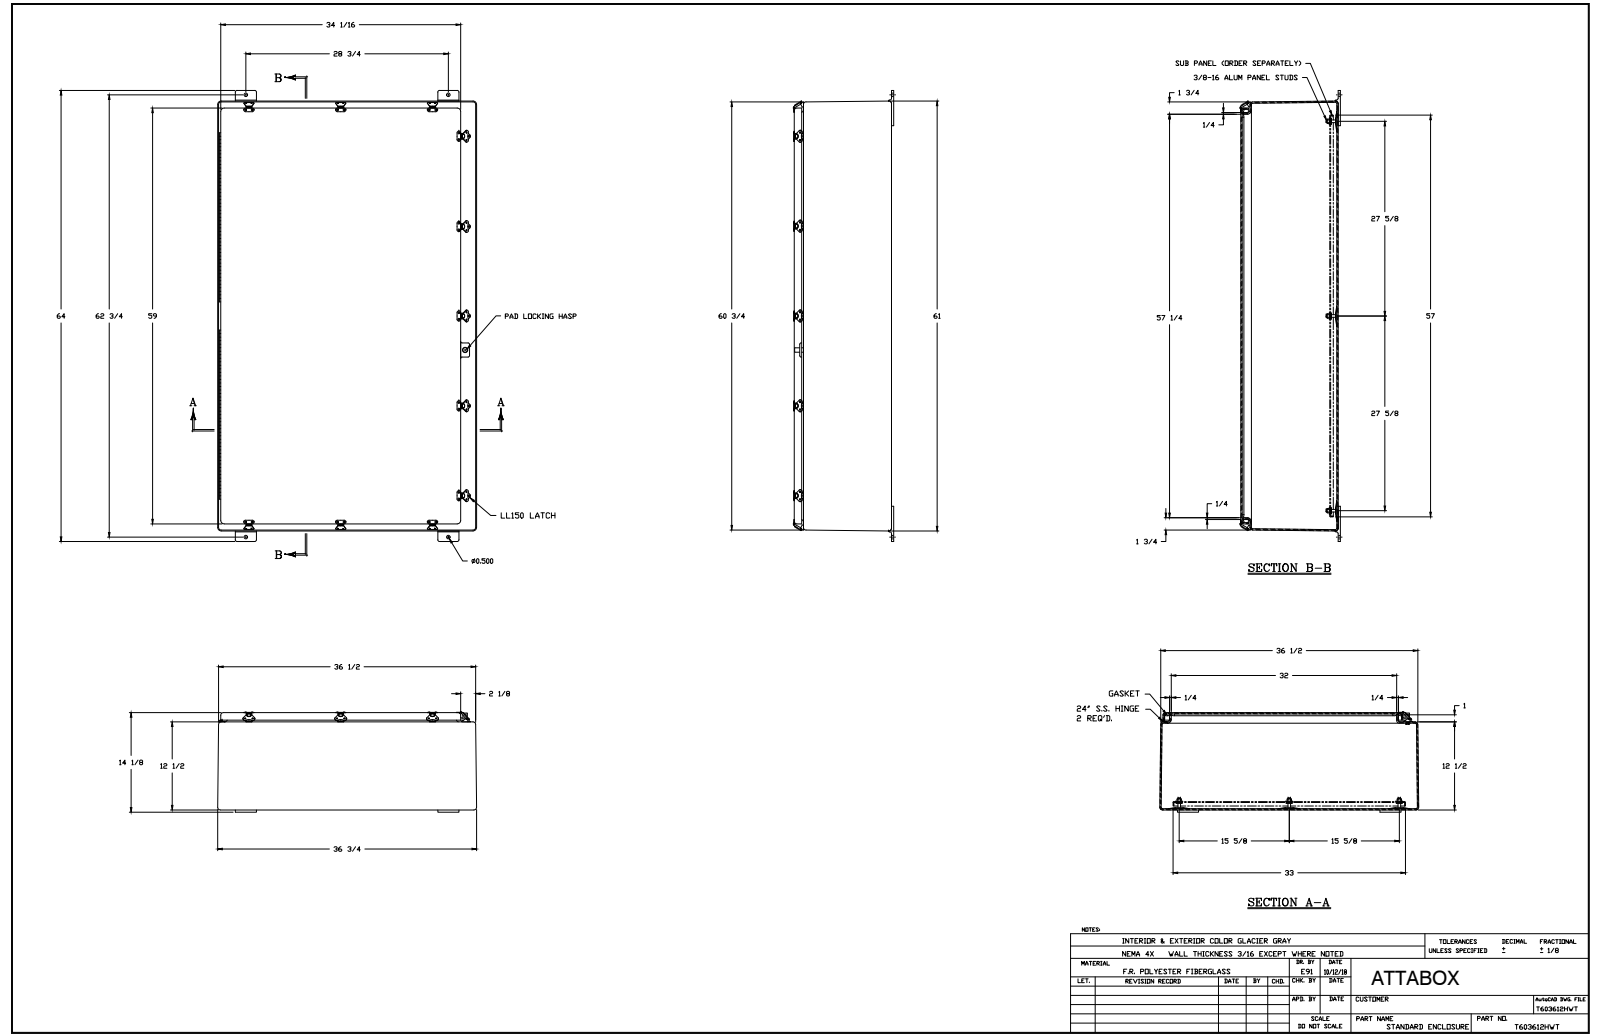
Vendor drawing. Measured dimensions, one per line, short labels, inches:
name: T603612HWT
written by: SolidWorks 2018 (AUTOMOTIVE_DESIGN)
unit: in
bodies: 127 solids, 3110 faces (1190 planar, 1300 cylindrical, 620 other)
size: 64 × 36.75 × 14.366
volume: 1 438 in³; area: 15 473 in²
holes: 54× ⌀0.13, 44× ⌀0.063, 22× ⌀0.138, 22× ⌀0.187, 20× ⌀0.14, 12× ⌀0.065, 8× ⌀0.201, 6× ⌀0.375, 4× ⌀0.065, 4× ⌀0.5, 3× ⌀0.135, 3× ⌀0.156
bosses: 44× ⌀0.14, 16× ⌀0.297, 11× ⌀0.5, 3× ⌀0.2, 2× ⌀0.25, 1× ⌀0.201, 1× ⌀0.135
rounds: 243× R0.01, 44× R0.03, 41× R0.312, 23× R0.375, 22× R0.21, 22× R1.186, 18× R0.25, 14× R0.038
face distances: 0.187, 0.25, 0.125, 13.813, 13.687, 13.563, 13.437, 36.562, 60.813, 36.75
hole spacings: 7.5, 13.031, 15, 27.5, 1, 20, 0.5, 12.5
